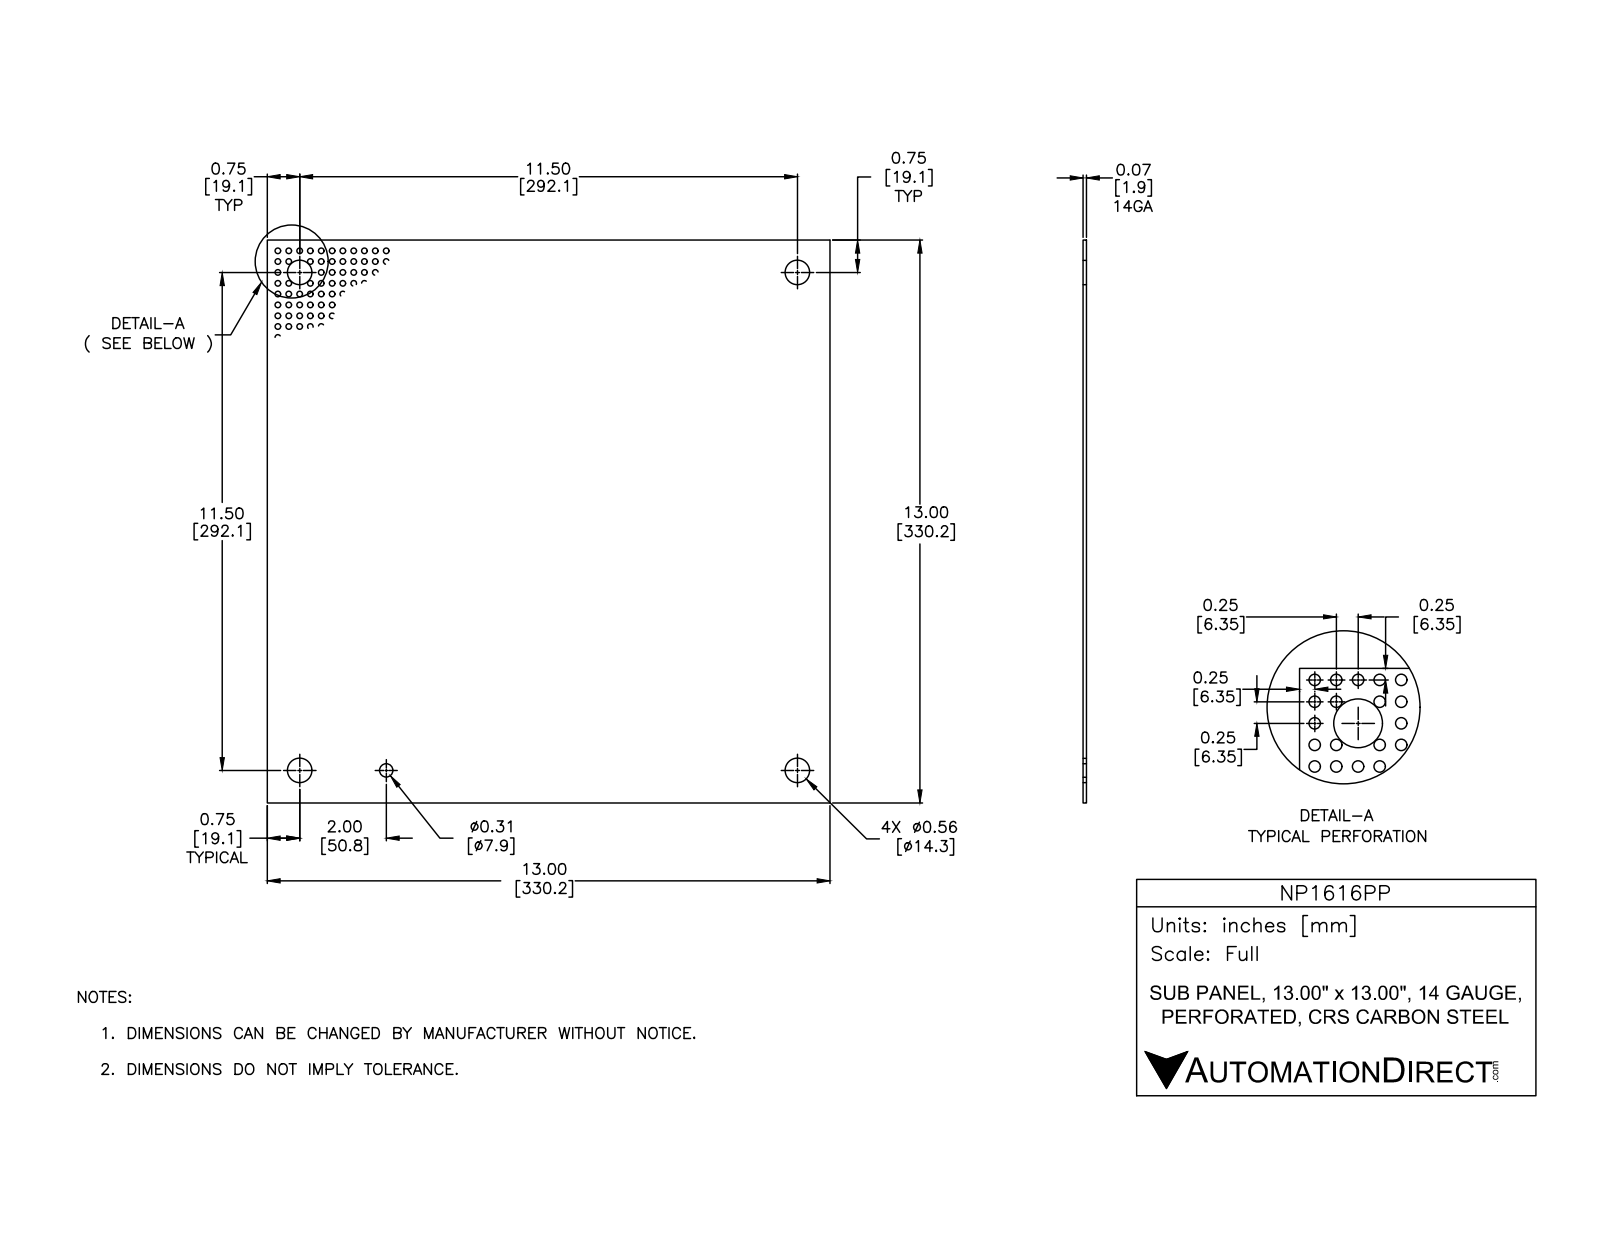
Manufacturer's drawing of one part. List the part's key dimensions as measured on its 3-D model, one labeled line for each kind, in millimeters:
Part name (STEP PRODUCT): NP1616PP
STEP written by: Autodesk Inventor 2012 (AUTOMOTIVE_DESIGN)
Units: millimetres
Bodies: 1 solid, 11 faces (6 planar, 5 cylindrical, 0 other)
Overall size (bounding box): 330.2 × 330.2 × 1.9
Volume: 203 700 mm³ · Surface area: 219 500 mm²
Round holes (diameter × count): ⌀14.3 ×4, ⌀7.9 ×1
Main face-to-face distances: 1.9, 330.2
Hole centre spacings: 285.8, 404.1, 50.8, 235, 290.2, 369.9
